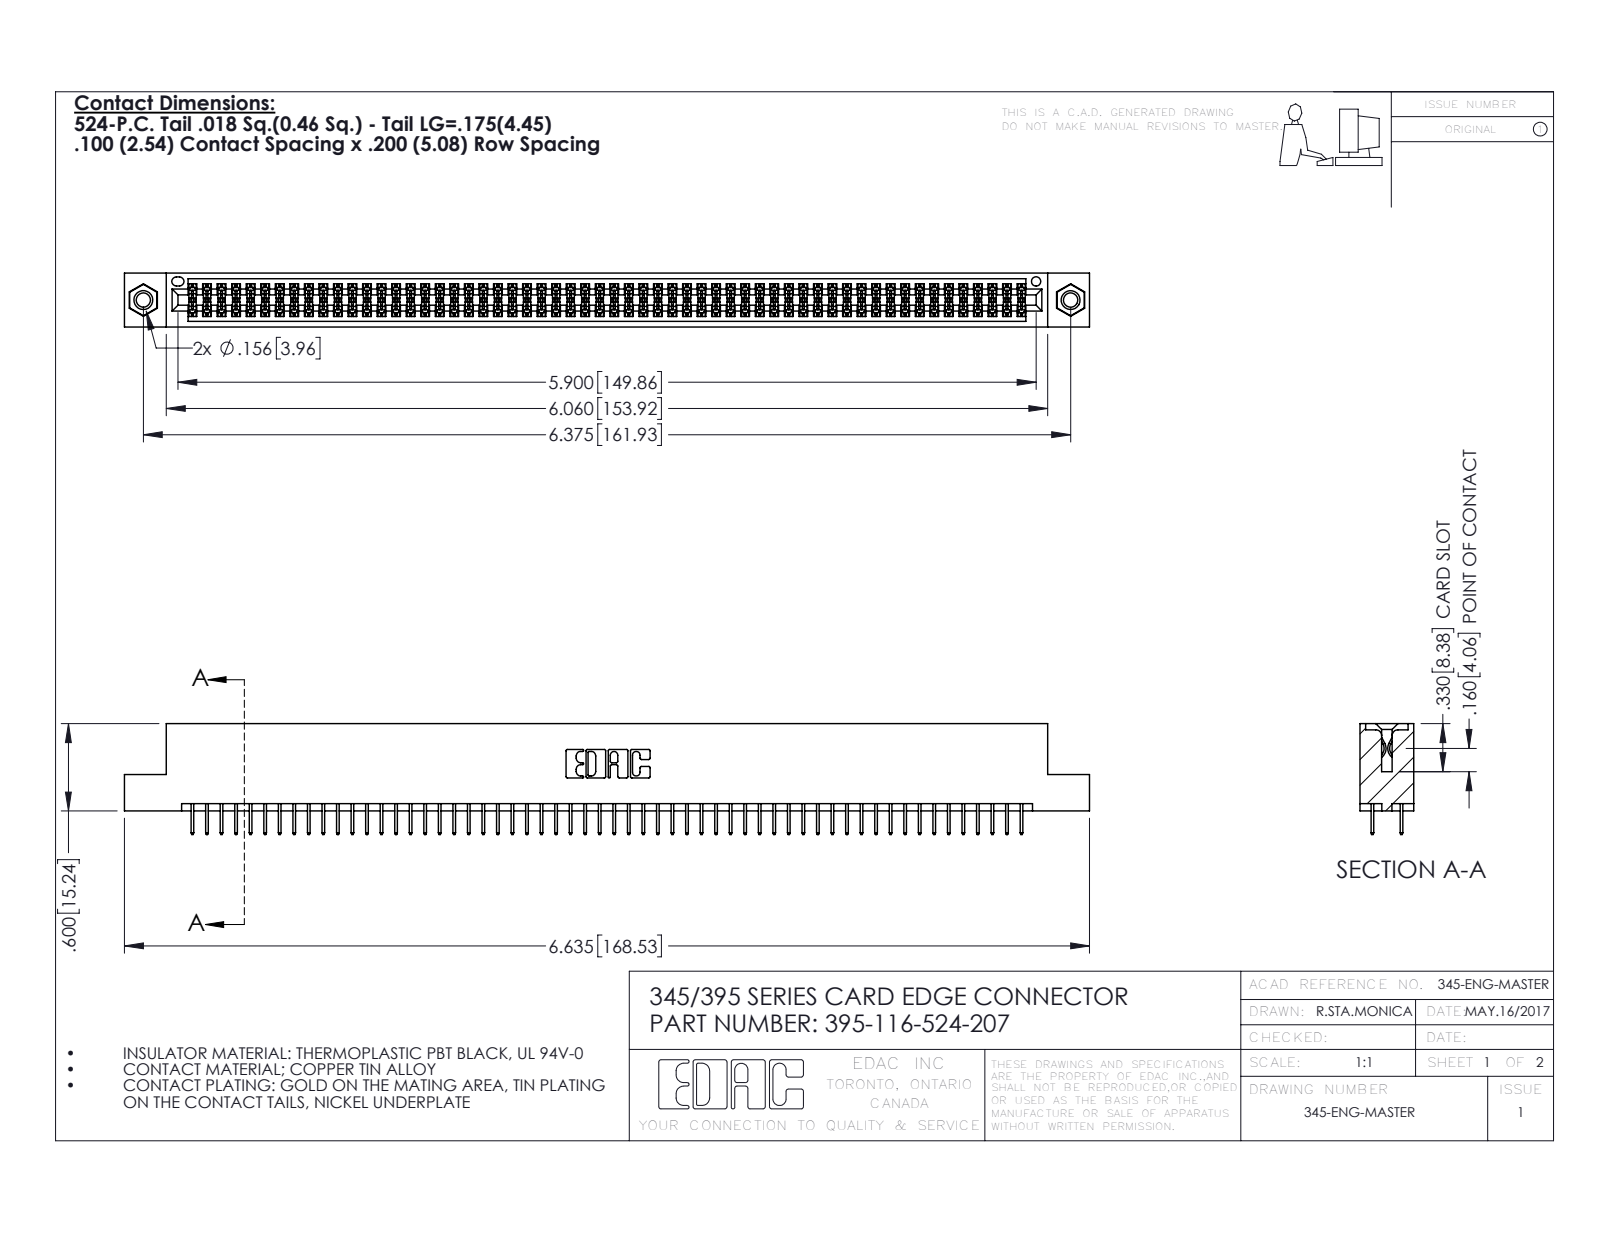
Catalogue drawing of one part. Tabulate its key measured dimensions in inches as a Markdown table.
| quantity | value |
| --- | --- |
| part name | 395-116-524-207; 345 Part_Flush Mounting Lugs - 0.156 Dia-TI; 345-250-001_345-250-005-103; 345-292-001_345-293-124 |
| STEP written by | SolidWorks 2016 (CONFIG_CONTROL_DESIGN) |
| units | inches |
| bodies | 119 solids, 6450 faces (4636 planar, 1798 cylindrical, 16 other) |
| overall size | 6.635 × 0.762 × 0.37 |
| volume | 0.997 in³ |
| surface area | 37.22 in² |
| round holes (diameter × count) | 0.098 × 2, 0.125 × 2, 0.156 × 2, 0.064 × 1 |
| round bosses / shafts (diameter × count) | 0.155 × 2 |
| partial cylindrical surfaces (radius × count) | 0.006 × 174, 0.01 × 22, 0.007 × 6, 0.031 × 6, 0.026 × 3, 0.014 × 2, 0.019 × 2, 0.022 × 2 |
| main face-to-face distances | 0.072, 0.298, 0.2, 0.37, 0.098, 0.272, 0.025, 0.225, 0.072, 0.175 |
| hole center spacings | 0.27, 6.139, 6.375 |
